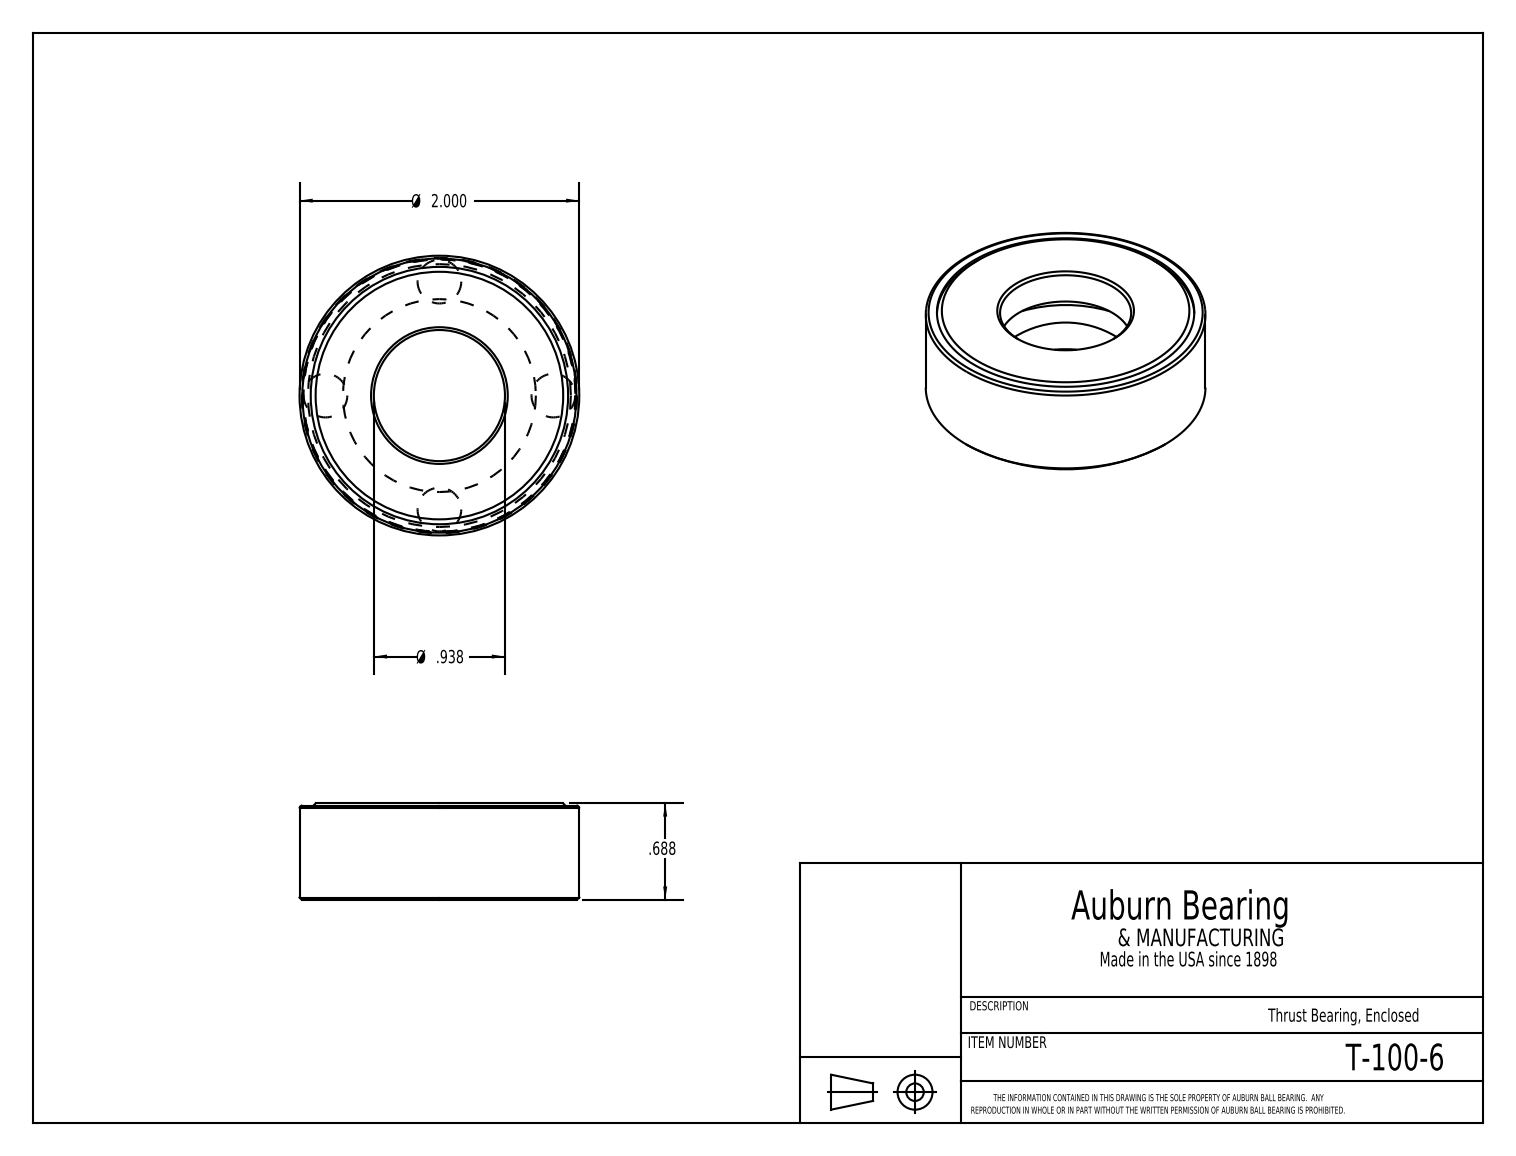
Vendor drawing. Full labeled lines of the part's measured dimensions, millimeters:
Part name (STEP PRODUCT): T-100-6
STEP written by: SolidWorks 2016 (CONFIG_CONTROL_DESIGN)
Units: millimetres
Bodies: 6 solids, 28 faces (9 planar, 7 cylindrical, 12 other)
Overall size (bounding box): 50.8 × 50.8 × 17.5
Volume: 19 170 mm³ · Surface area: 13 660 mm²
Round holes (diameter × count): ⌀23.8 ×1, ⌀46.7 ×1, ⌀49.8 ×1
Round bosses / shafts (diameter × count): ⌀50.8 ×1, ⌀49.4 ×1
Main face-to-face distances: 6.4, 11.1, 17.4, 4.7, 16.6, 10.2, 5.5, 0.9, 17.1, 10.7
